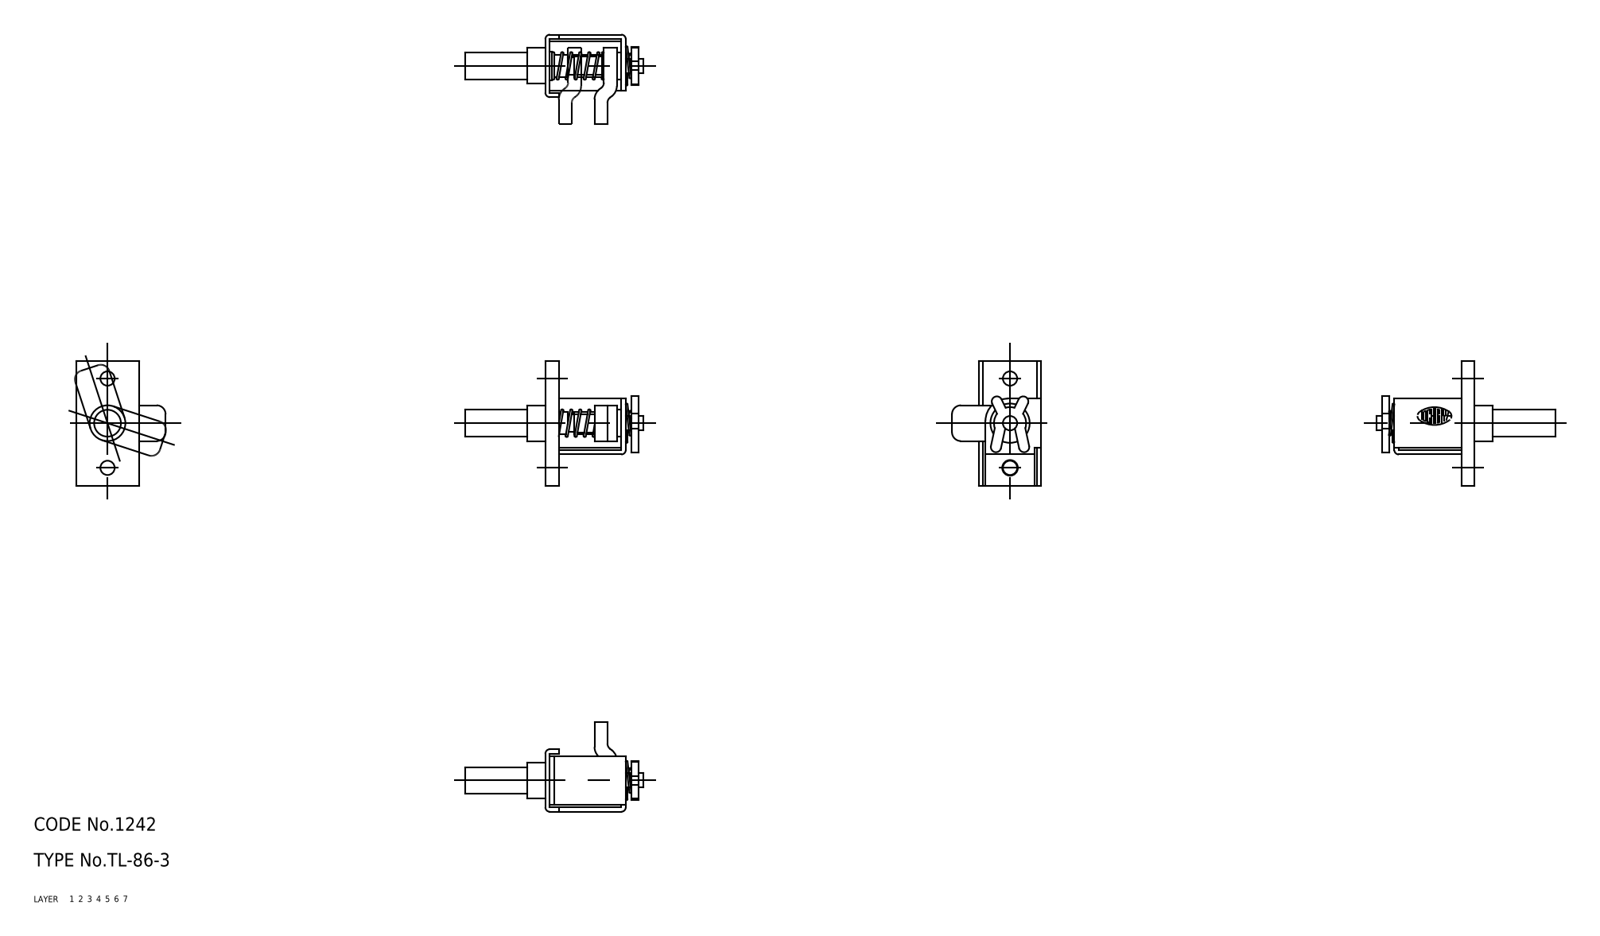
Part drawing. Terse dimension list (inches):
name: spring_2; spring_1; retainer; knob (+4 more)
written by: CADfix (AUTOMOTIVE_DESIGN)
unit: in
bodies: 7 solids, 251 faces (0 planar, 0 cylindrical, 251 other)
size: 1.575 × 1.102 × 0.787
volume: 0.148 in³; area: 6.136 in²
